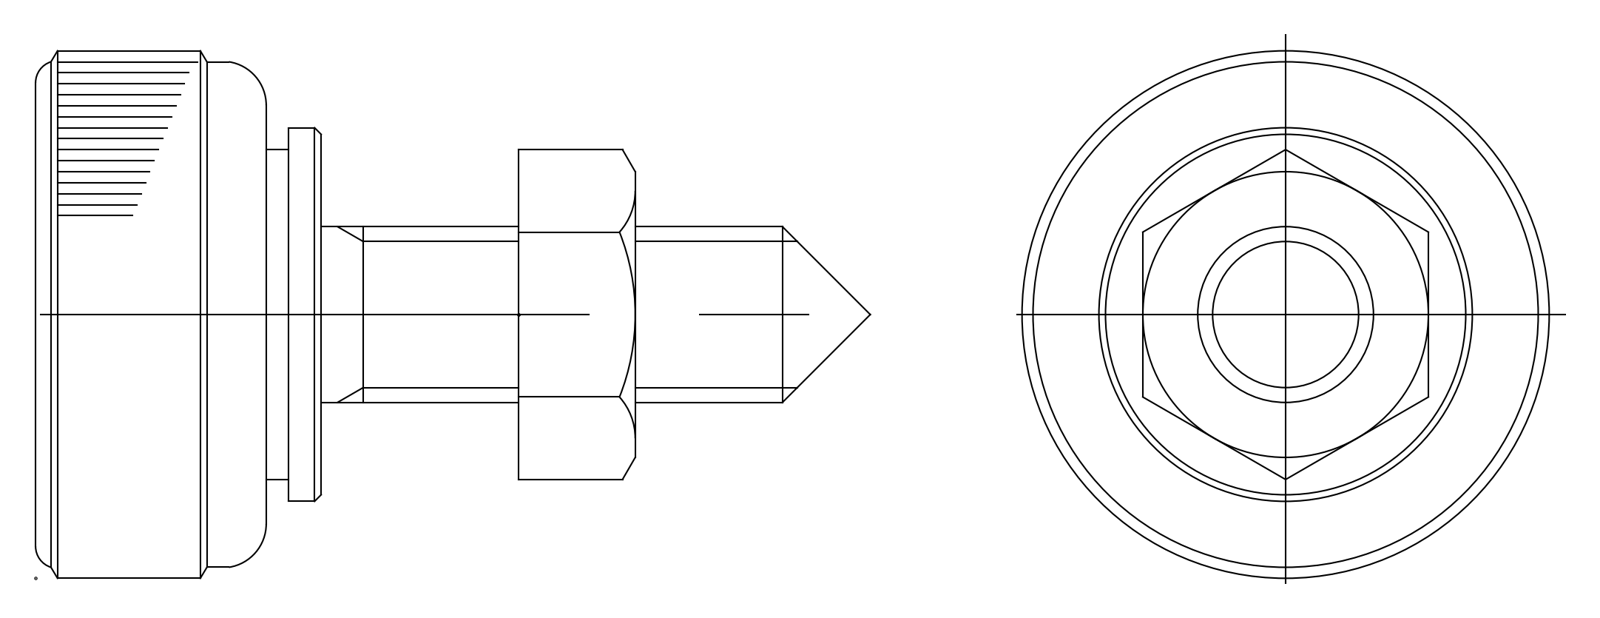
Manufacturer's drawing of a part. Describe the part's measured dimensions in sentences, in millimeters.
The part is named "THA_340SUS_24_8_Nツマミ; M8ナット". Its 3-D file was written by "spGate 20.6.3 (****-****-****-****) (AUTOMOTIVE_DESIGN)". It is 2 solids with 42 faces: 12 planar, 12 cylindrical and 18 other. Overall it measures 38 by 24 by 24 millimeters. Its volume is 6 805 cubic millimeters and its surface area 2 971 square millimeters. Round holes: 1 of diameter 8. Round bosses or shafts: 1 of diameter 24, 1 of diameter 23, 1 of diameter 17, 1 of diameter 15. The main face-to-face distances are 13, 10.5, 2.5, 20.41, 9.91, 7.41, 26.91, 16.41, 13.91, 6.5.
